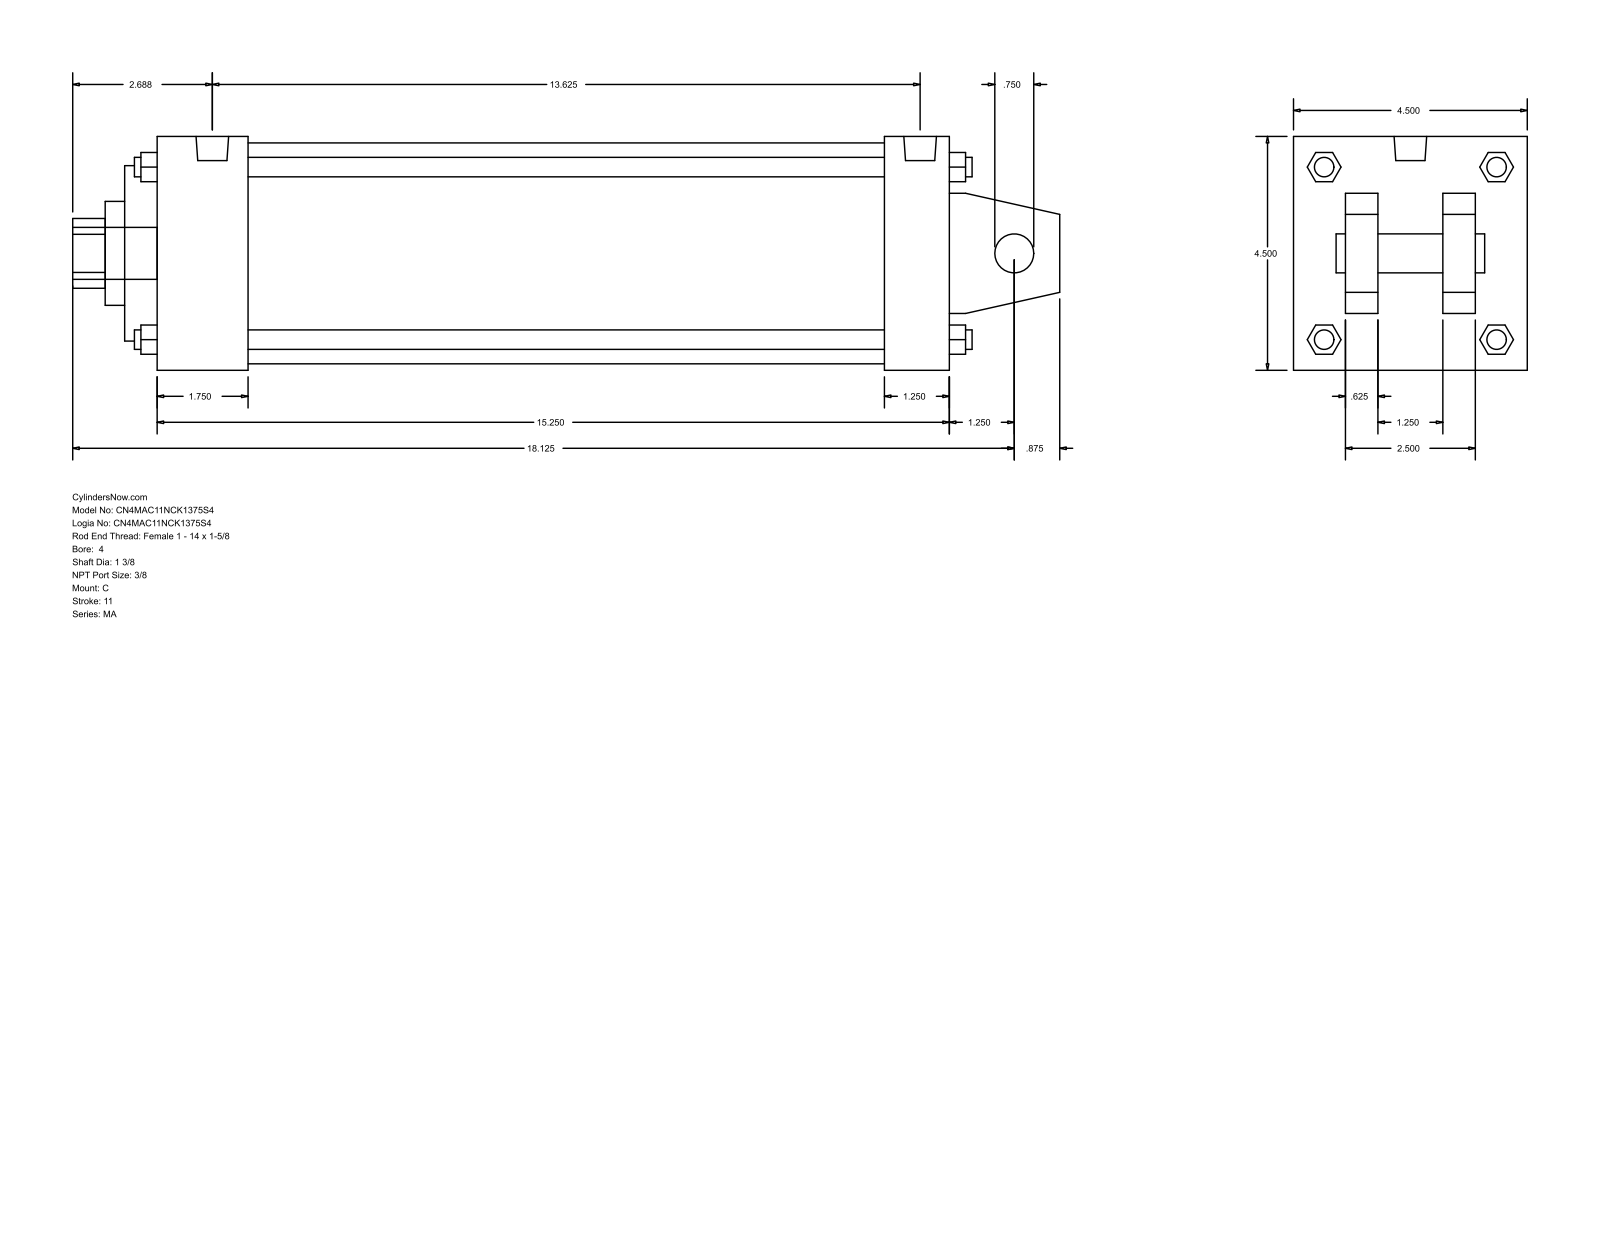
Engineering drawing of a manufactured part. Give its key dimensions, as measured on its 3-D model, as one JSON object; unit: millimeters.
{"part_name": "MA_C__0400_1.375", "step_written_by": "GSSL Pune (CONFIG_CONTROL_DESIGN)", "units": "millimeters", "bodies": {"solids": 0, "faces": 141, "planar": 109, "cylindrical": 32, "other": 0}, "overall_size": [482.6, 114.3, 114.3], "round_holes": [[19.05, 1], [34.92, 1], [50.8, 1], [85.72, 1], [107.95, 1]], "round_bosses_or_shafts": [[11.11, 4], [9.53, 4], [15.93, 2], [25.4, 1]], "partial_cylinders_radius": [[17.06, 1]], "face_to_face_distances": [114.3, 15.87, 387.35, 73.03, 41.27, 25.4, 88.9, 47.63, 403.22, 371.48]}
